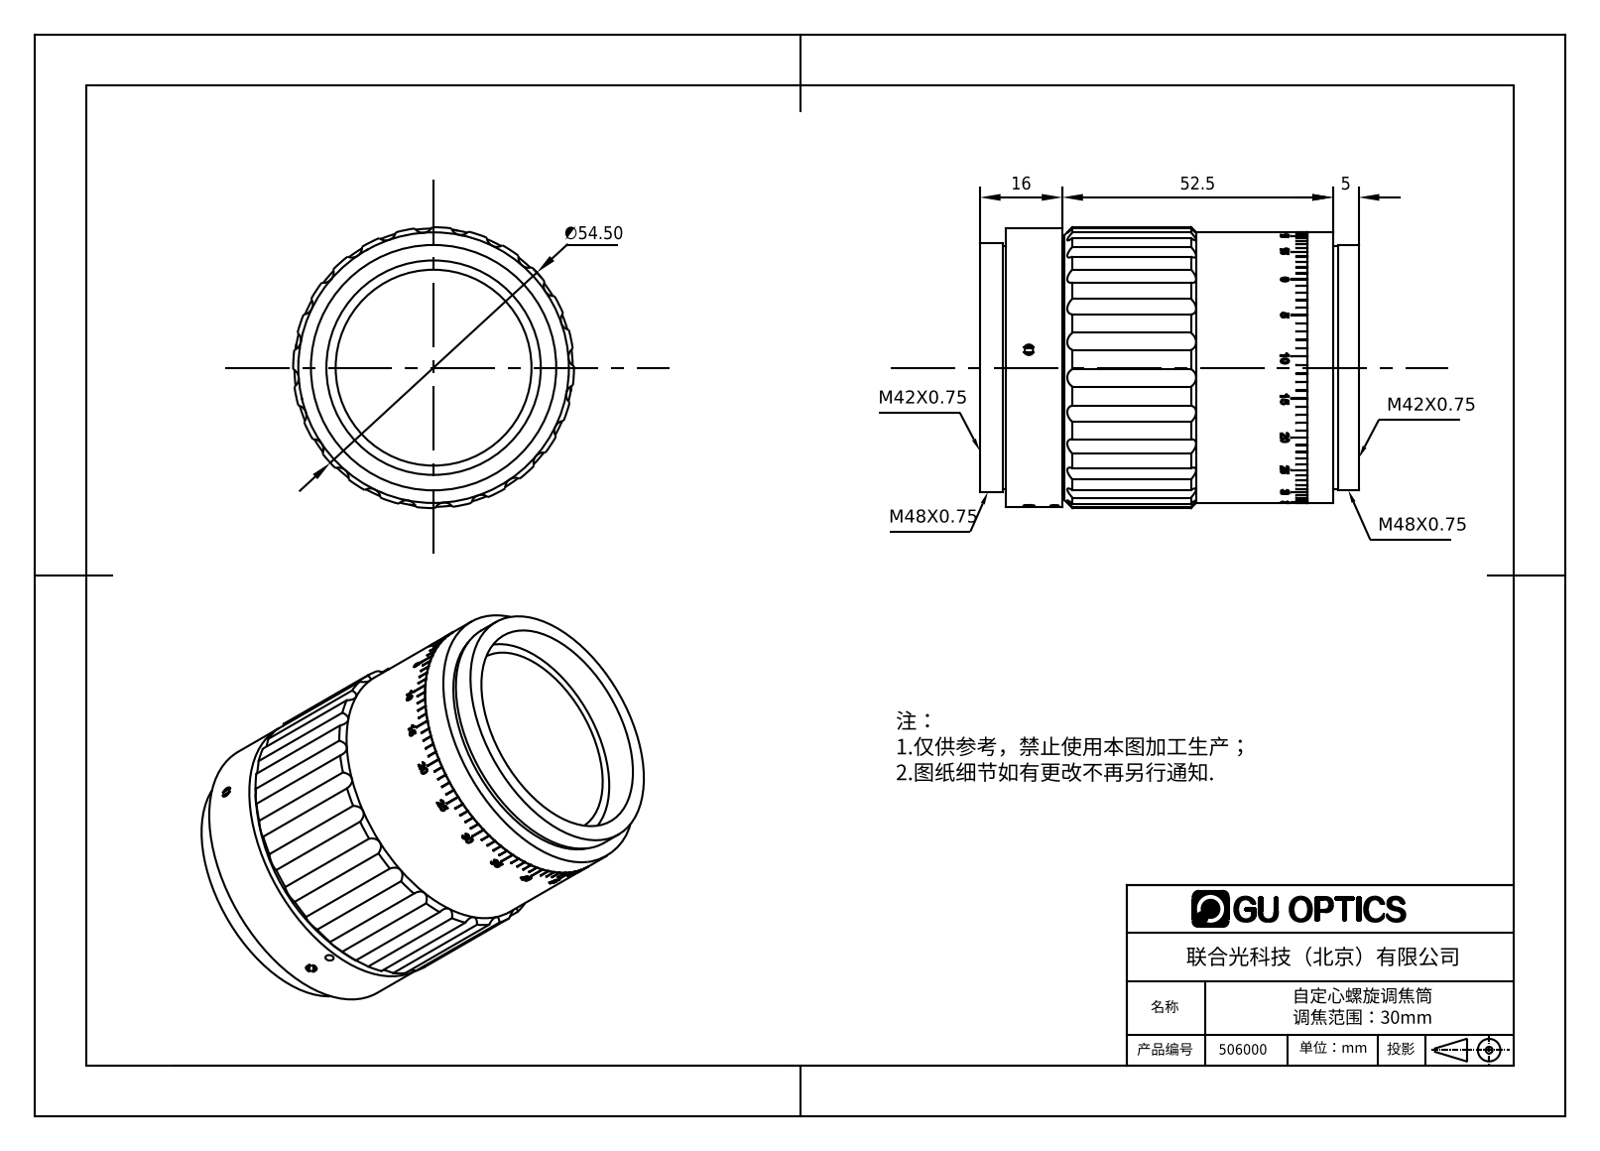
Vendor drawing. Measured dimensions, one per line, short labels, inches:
name: 506000定位筒; 506000调教手轮; 506000锁紧环; 506000自定心连动圈 (+2 more)
written by: SolidWorks 2016 (AUTOMOTIVE_DESIGN)
unit: in
bodies: 8 solids, 1069 faces (347 planar, 380 cylindrical, 342 other)
size: 2.894 × 2.146 × 2.146
volume: 4.183 in³; area: 94.21 in²
holes: 5× ⌀0.063, 3× ⌀0.083, 1× ⌀1.496, 1× ⌀1.614, 1× ⌀1.638, 1× ⌀1.732, 1× ⌀1.752, 1× ⌀1.76, 1× ⌀1.878, 1× ⌀1.949, 1× ⌀2.008
bosses: 4× ⌀0.081, 4× ⌀0.079, 1× ⌀2.126, 1× ⌀2.067, 1× ⌀1.992, 1× ⌀1.898, 1× ⌀1.89, 1× ⌀1.874
rounds: 24× R0.079, 4× R0.876, 3× R0.866, 1× R1.033, 1× R1.073
face distances: 0.197, 0.472, 0.079, 0.394, 2.697, 0.039, 2.5, 2.224, 0.018, 2.01
hole spacings: 0.197
